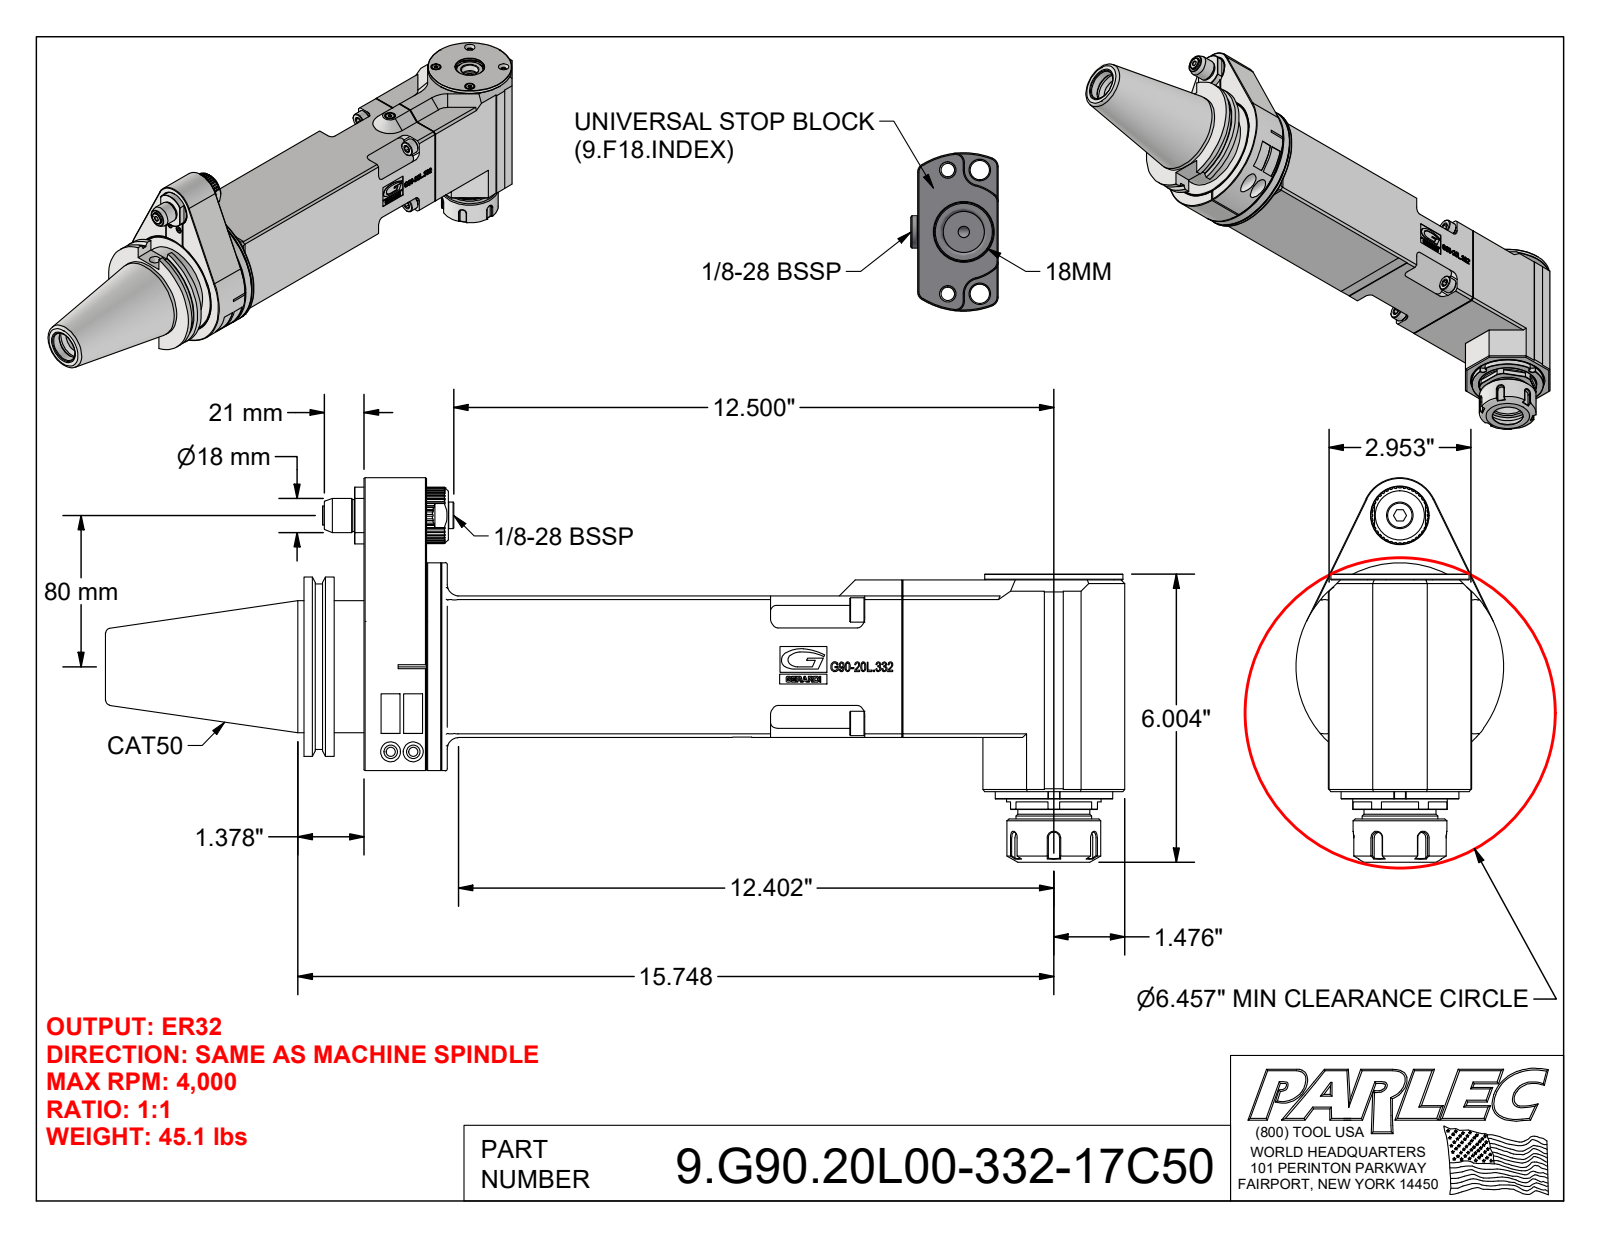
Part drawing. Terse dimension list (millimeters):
name: 9.G90.20L00-332-17C50; 9_G90_20L00-332; 9_GA2_458_1 (Classic, Type 2, Cat50, 80mm)
written by: Autodesk Inventor 2022 (AUTOMOTIVE_DESIGN)
unit: mm
bodies: 20 solids, 1499 faces (731 planar, 264 cylindrical, 504 other)
size: 539.3 × 203.5 × 110
volume: 2 843 000 mm³; area: 323 400 mm²
holes: 14× ⌀5, 4× ⌀4.2, 4× ⌀8.5, 3× ⌀6, 2× ⌀4, 2× ⌀4.5, 2× ⌀7, 2× ⌀10.5, 2× ⌀15, 1× ⌀3.3, 1× ⌀9, 1× ⌀9.2
bosses: 4× ⌀13, 2× ⌀10, 2× ⌀7.8, 1× ⌀110, 1× ⌀98.4, 1× ⌀91.3, 1× ⌀89.5, 1× ⌀73
rounds: 10× R3, 8× R4, 6× R2.5, 4× R6, 2× R2.2, 2× R5.7, 1× R2, 1× R2.9
face distances: 75, 33, 8, 25, 15.9, 5, 3, 11.5, 0.5, 4.5
hole spacings: 47.5, 24.6, 67.2, 82.3, 91.8, 5.5, 13.7, 20.8
